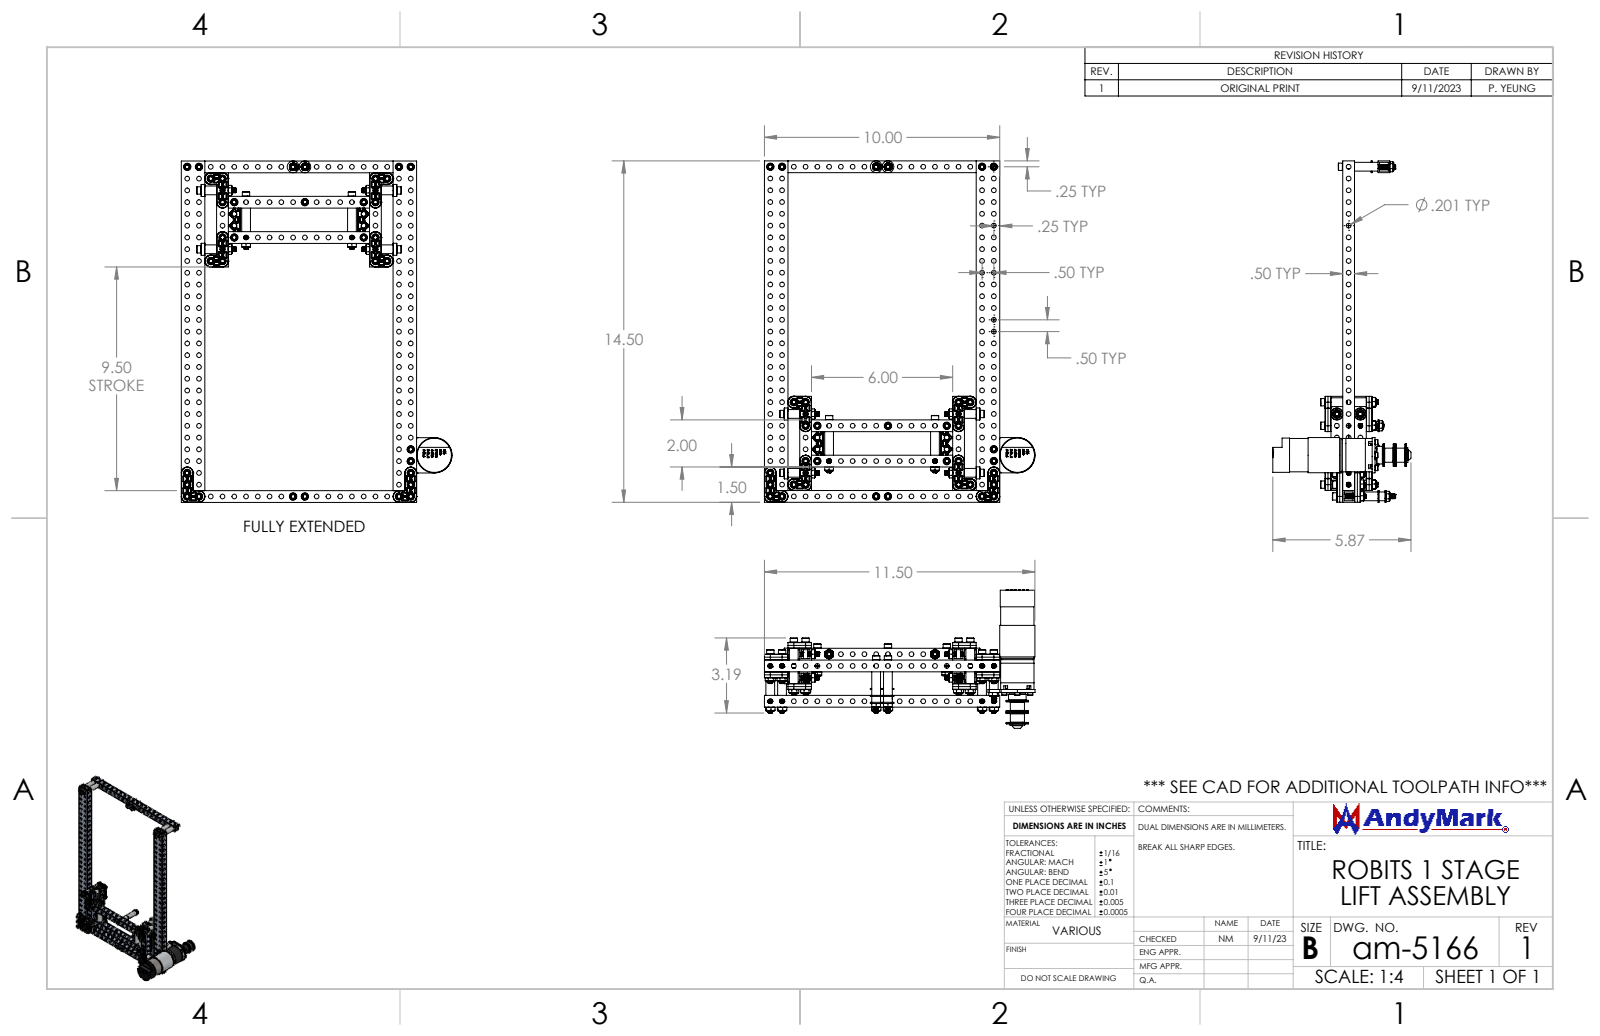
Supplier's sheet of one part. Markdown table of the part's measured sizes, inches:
| quantity | value |
| --- | --- |
| part name | am-5001-0600 RoBits 0.5x0.5x6.0 Tube; am-3444 6mm D to 375IN Hex Adapter; am-1696 0.194 ID 0.375 OD 1.000 Long Nylon Spacer; am-5027 Robits Spool 375 Hex (+8 more) |
| STEP written by | SolidWorks 2022 (AUTOMOTIVE_DESIGN) |
| units | inches |
| bodies | 560 solids, 21503 faces (3006 planar, 8186 cylindrical, 10311 other) |
| overall size | 14.5 × 11.5 × 5.875 |
| volume | 24.92 in³ |
| surface area | 633.8 in² |
| round holes (diameter × count) | 0.201 × 292, 0.164 × 180, 0.161 × 41, 0.239 × 41, 0.192 × 25, 0.125 × 13, 0.098 × 10, 0.125 × 9, 0.197 × 8, 0.323 × 8, 0.386 × 8, 0.219 × 5 |
| round bosses / shafts (diameter × count) | 0.19 × 42, 0.312 × 39, 0.375 × 25, 0.512 × 8, 0.217 × 8, 0.118 × 8, 0.5 × 5, 0.093 × 4 |
| partial cylindrical surfaces (radius × count) | 0.01 × 624, 0.082 × 45, 0.064 × 34, 0.062 × 14, 0.163 × 12, 0.028 × 4, 0.047 × 4, 0.059 × 4 |
| main face-to-face distances | 0.063, 0.5, 0.437, 1, 1.5, 0.937, 0.375, 0.563, 1.063, 1.437 |
| hole center spacings | 1, 0.5, 1.5, 2.5, 2, 4.5, 3, 3.5 |
